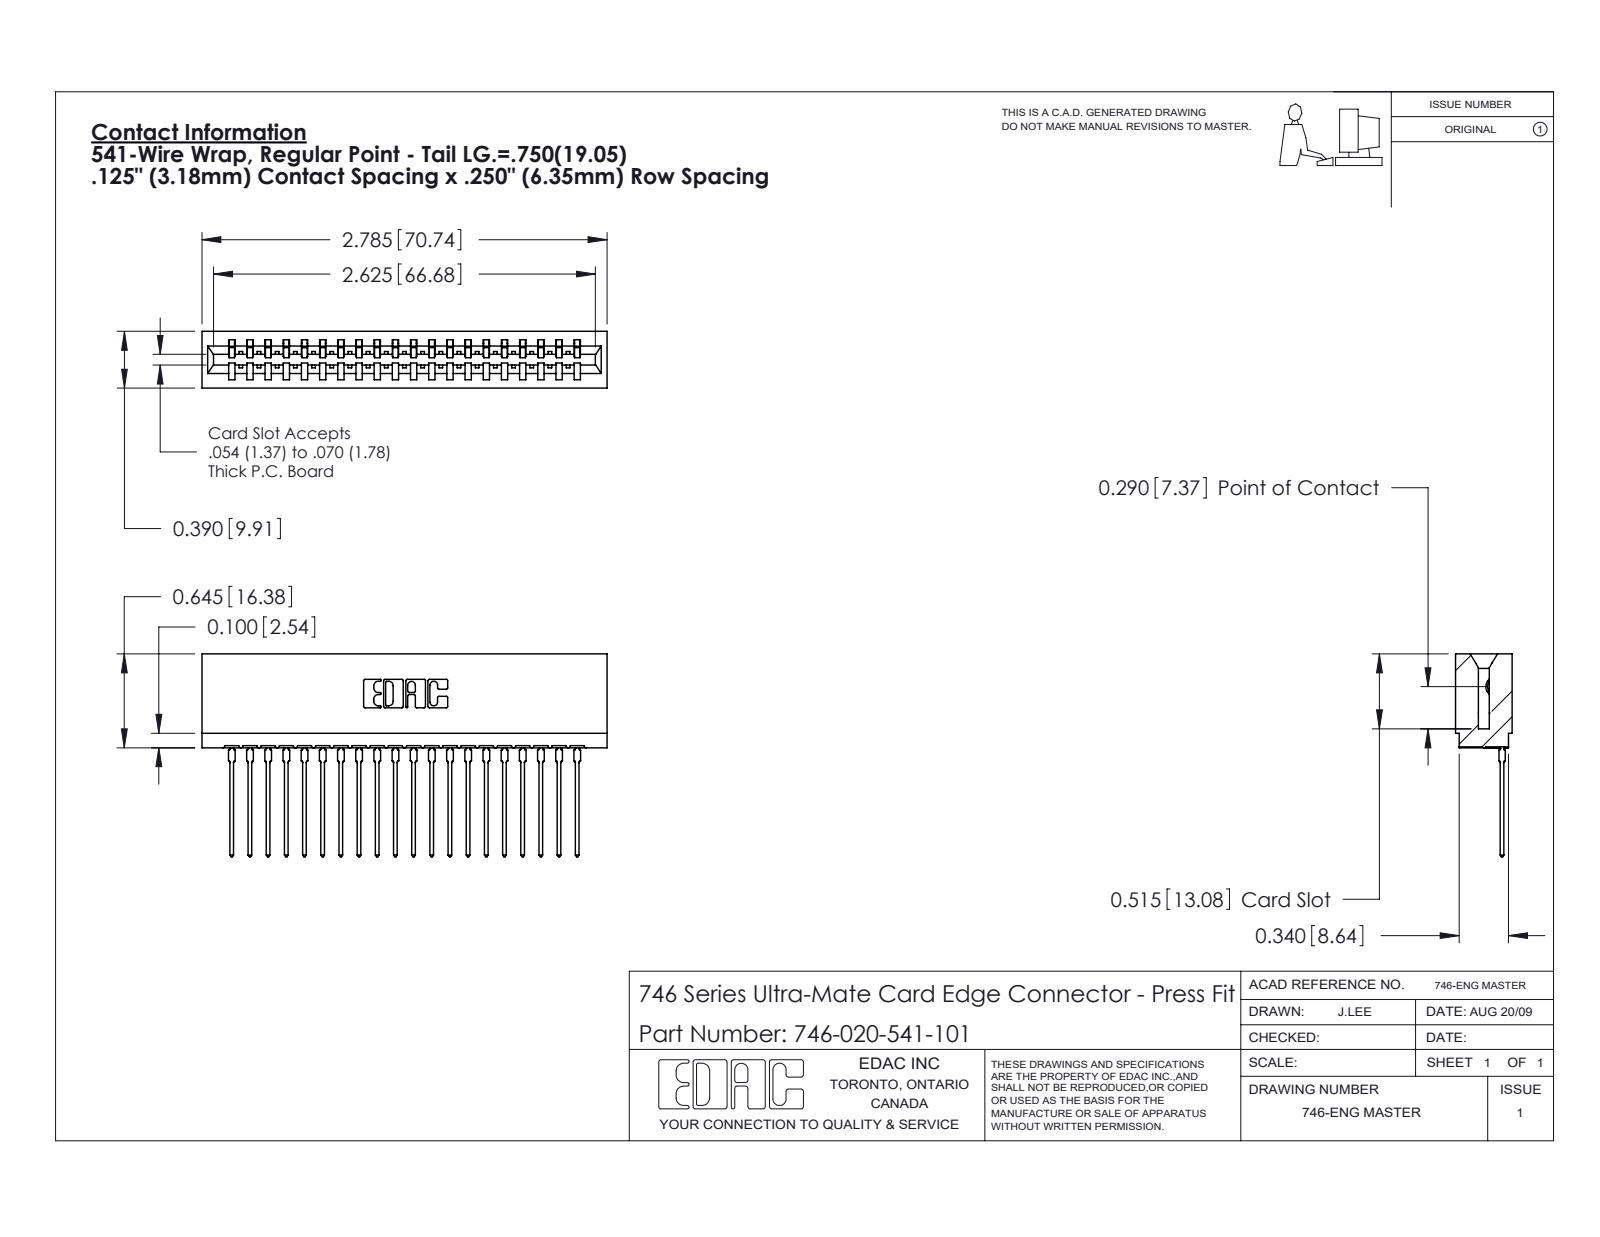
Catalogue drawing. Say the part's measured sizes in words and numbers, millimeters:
The part is named "746-020-541-101; 746-292-001_541; 746 Part_.515 Slot Depth - 01". Its 3-D file was written by "SolidWorks 2020 (CONFIG_CONTROL_DESIGN)". It is 21 solids with 2257 faces: 1315 planar, 422 cylindrical and 520 other. Overall it measures 70.7 by 35.4 by 9.9 millimeters. Its volume is 7 640 cubic millimeters and its surface area 11 430 square millimeters. Partial cylindrical surfaces (rounded edges, fillets, slot ends): 40 of radius 0.5, 22 of radius 0.3, 21 of radius 0.4, 6 of radius 0.2, 6 of radius 0.8, 4 of radius 0.1, 4 of radius 0.3, 3 of radius 0.7. The main face-to-face distances are 6.4, 1.4, 8.5, 9.9, 12.7, 0.6, 7.8, 2.1, 9.5, 3.2.
